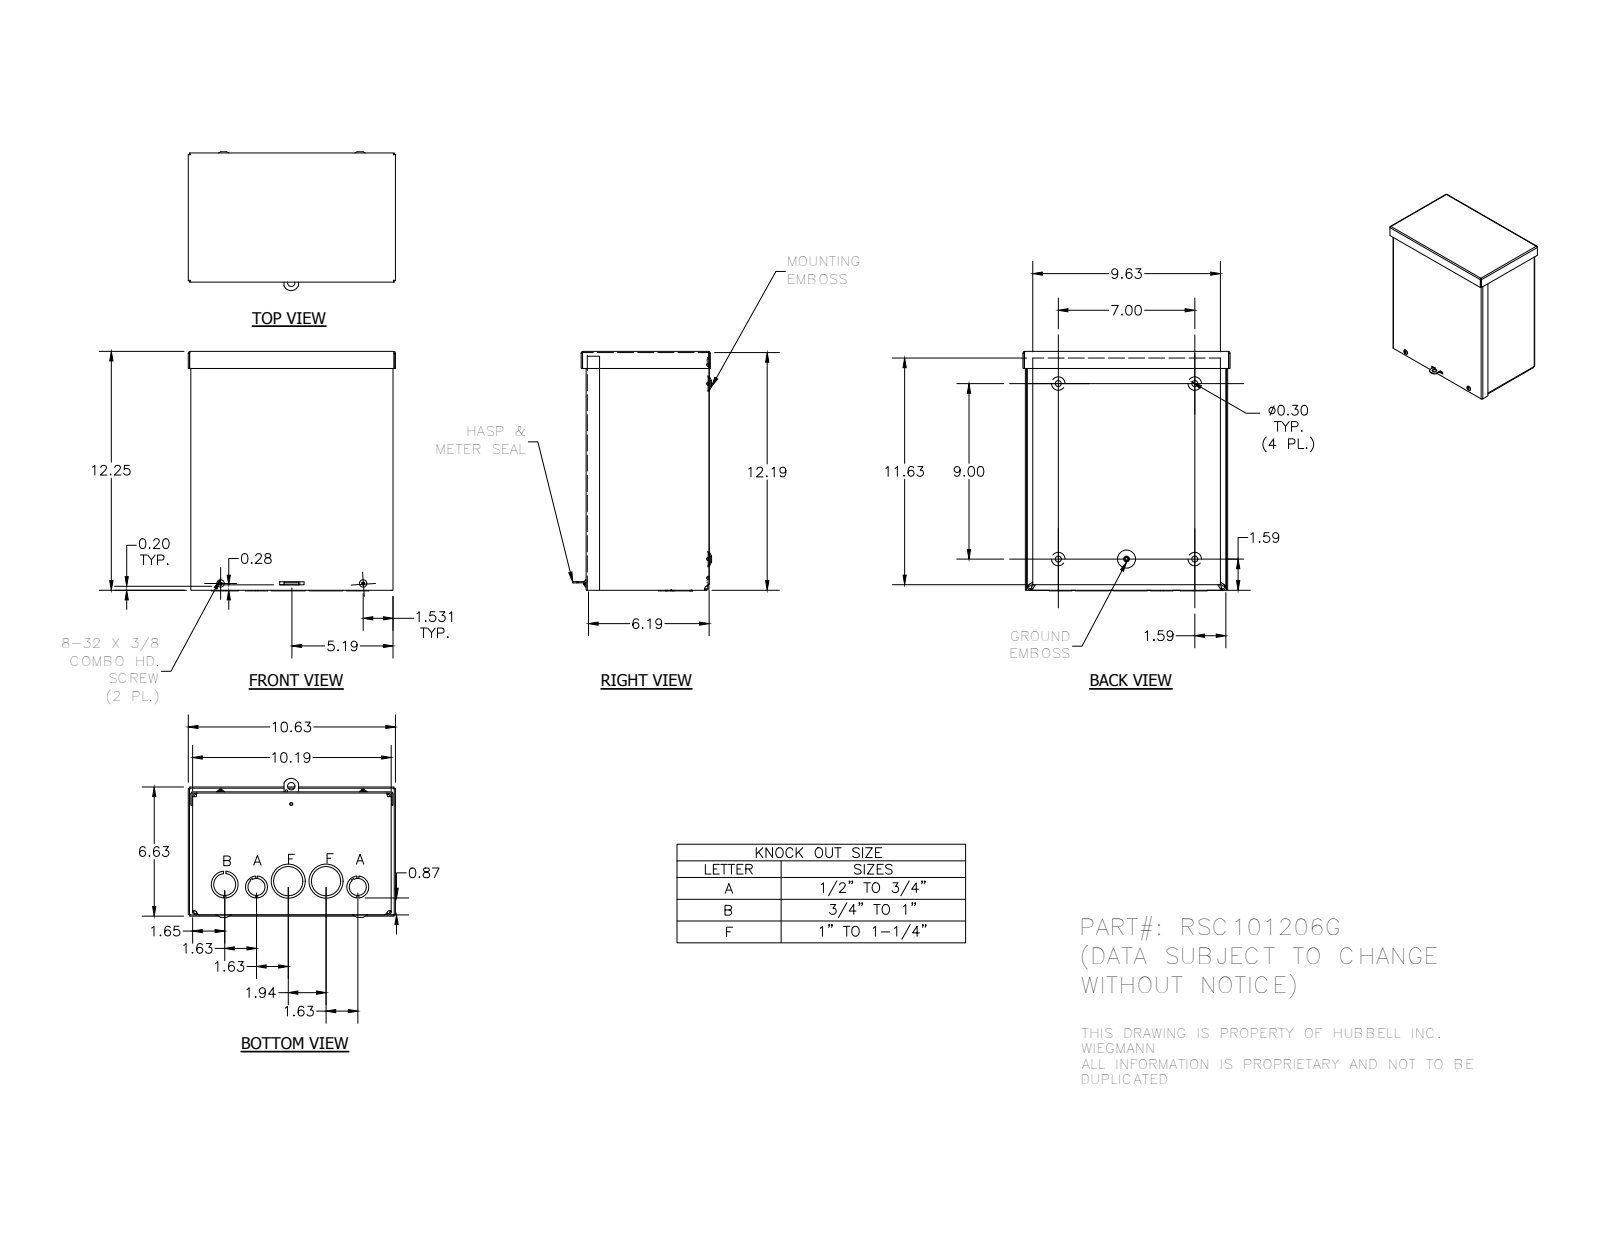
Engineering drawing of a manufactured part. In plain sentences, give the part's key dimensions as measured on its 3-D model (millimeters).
The part is named "RSC101206G_WRAP; RSC1012G_LID; RSC1006G_CAP; 3183 (+4 more)". Its 3-D file was written by "Autodesk Inventor 2014 (AUTOMOTIVE_DESIGN)". It is 7 solids with 518 faces: 245 planar, 129 cylindrical and 144 other. Overall it measures 311.93 by 269.88 by 180.97 millimeters. Its volume is 696 364 cubic millimeters and its surface area 895 786 square millimeters. Round holes: 4 of diameter 7.62, 4 of diameter 7.95, 3 of diameter 28.57, 2 of diameter 3.17, 2 of diameter 3.76, 2 of diameter 22.22, 2 of diameter 38.1, 2 of diameter 44.45, 1 of diameter 3.96, 1 of diameter 4.19, 1 of diameter 9.52, 1 of diameter 34.92. Round bosses or shafts: 2 of diameter 9.75, 2 of diameter 4.17, 1 of diameter 5.8. Partial cylindrical surfaces (rounded edges, fillets, slot ends): 10 of radius 0.25, 8 of radius 0.79, 8 of radius 2.37, 8 of radius 3.17, 8 of radius 4.75, 4 of radius 0.79, 4 of radius 1.4, 4 of radius 1.57. The main face-to-face distances are 1.58, 1.57, 257.19, 158.73, 157.15, 1.59, 307.99, 160.32, 158.74, 3.15. The hole center spacings are 27.24, 32.03, 42.07, 88.9, 90.99, 177.8, 185.75, 228.6.
